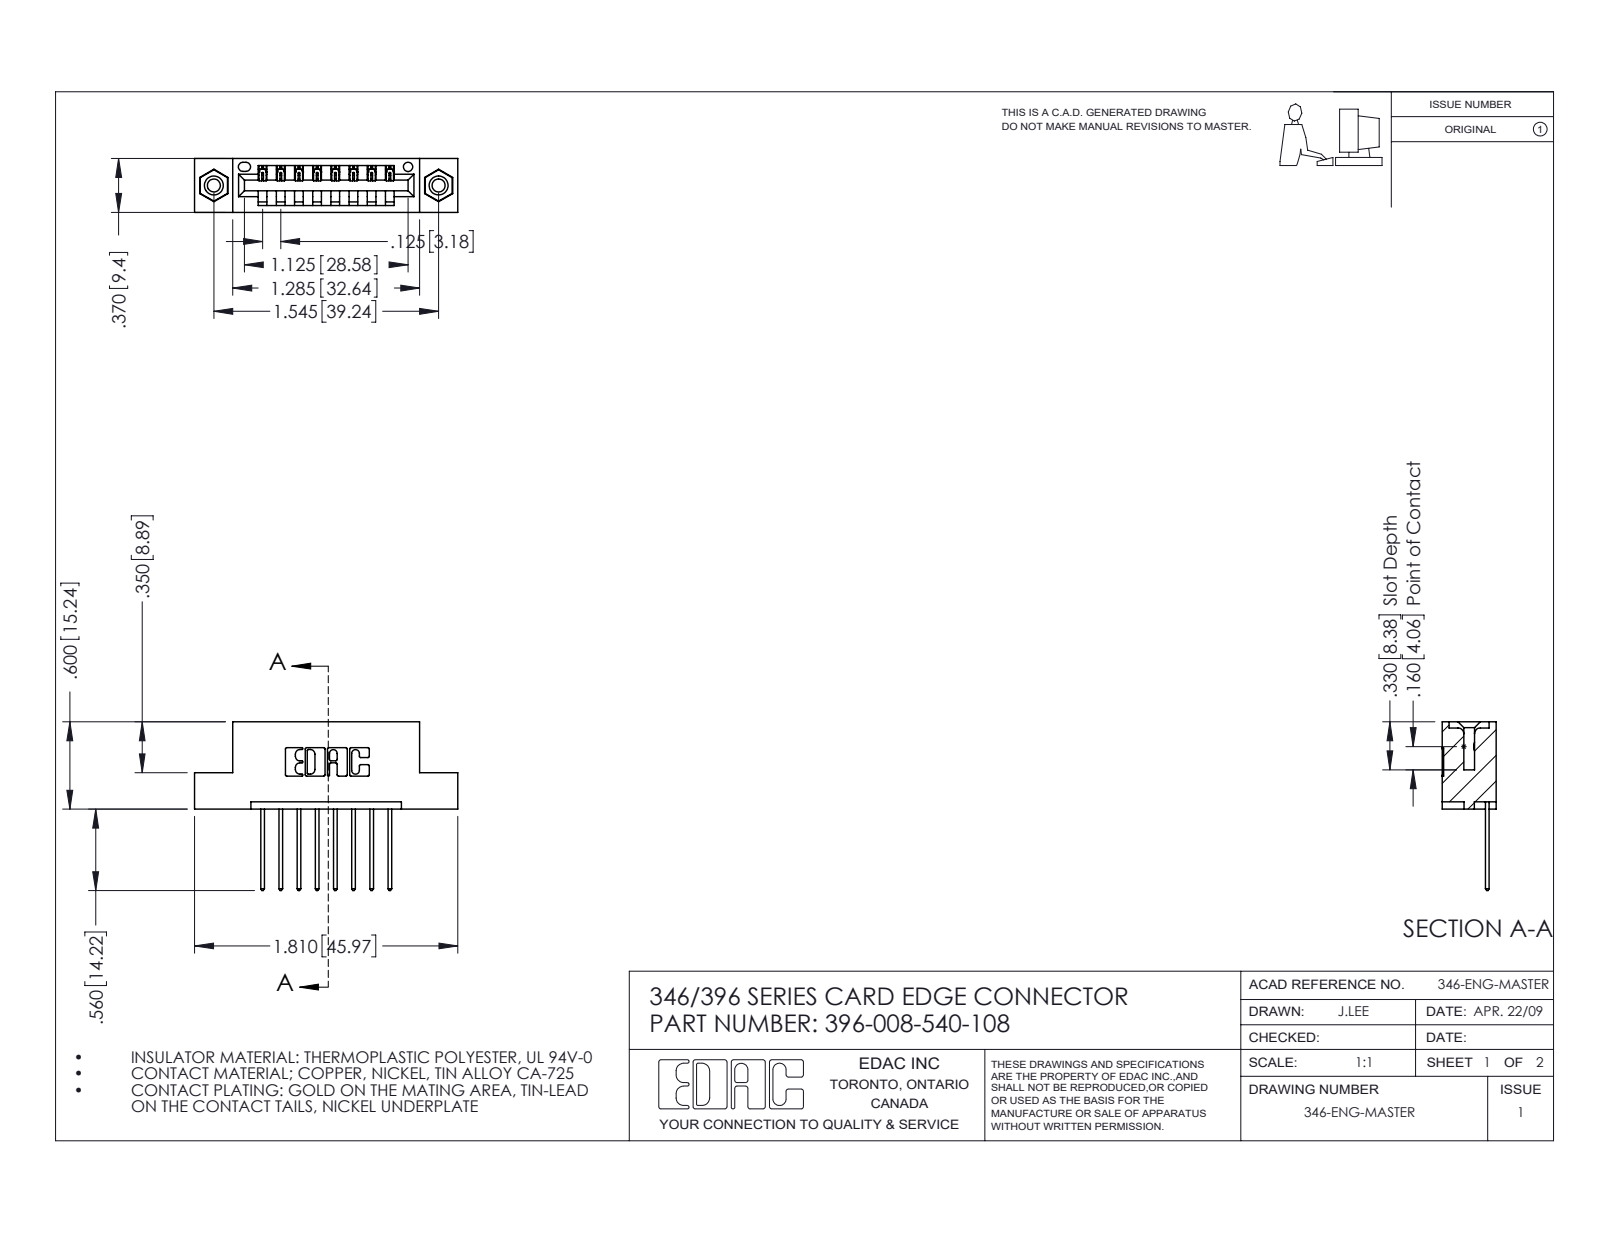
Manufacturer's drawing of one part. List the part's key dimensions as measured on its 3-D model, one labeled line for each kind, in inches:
Part name (STEP PRODUCT): 345-250-001_345-250-003-102; 345-292-001_345-293-140; 346 Part_Flush Mounting Lugs - 0.156 Dia-TI; 396-008-540-108
STEP written by: SolidWorks 2016 (CONFIG_CONTROL_DESIGN)
Units: inches
Bodies: 11 solids, 646 faces (428 planar, 202 cylindrical, 16 other)
Overall size (bounding box): 1.81 × 1.16 × 0.37
Volume: 0.255 in³ · Surface area: 7.668 in²
Round holes (diameter × count): ⌀0.089 ×2, ⌀0.125 ×2, ⌀0.156 ×2, ⌀0.064 ×1
Round bosses / shafts (diameter × count): ⌀0.155 ×2
Partial cylindrical surfaces — rounded edges, fillets, slot ends (radius × count): R0.01 ×22, R0.006 ×16, R0.01 ×16, R0.007 ×6, R0.031 ×6, R0.026 ×3, R0.031 ×2, R0.04 ×2
Main face-to-face distances: 0.25, 0.048, 0.322, 0.37, 0.072, 0.298, 0.025, 0.5, 0.148, 0.222
Hole centre spacings: 0.246, 1.341, 1.545
